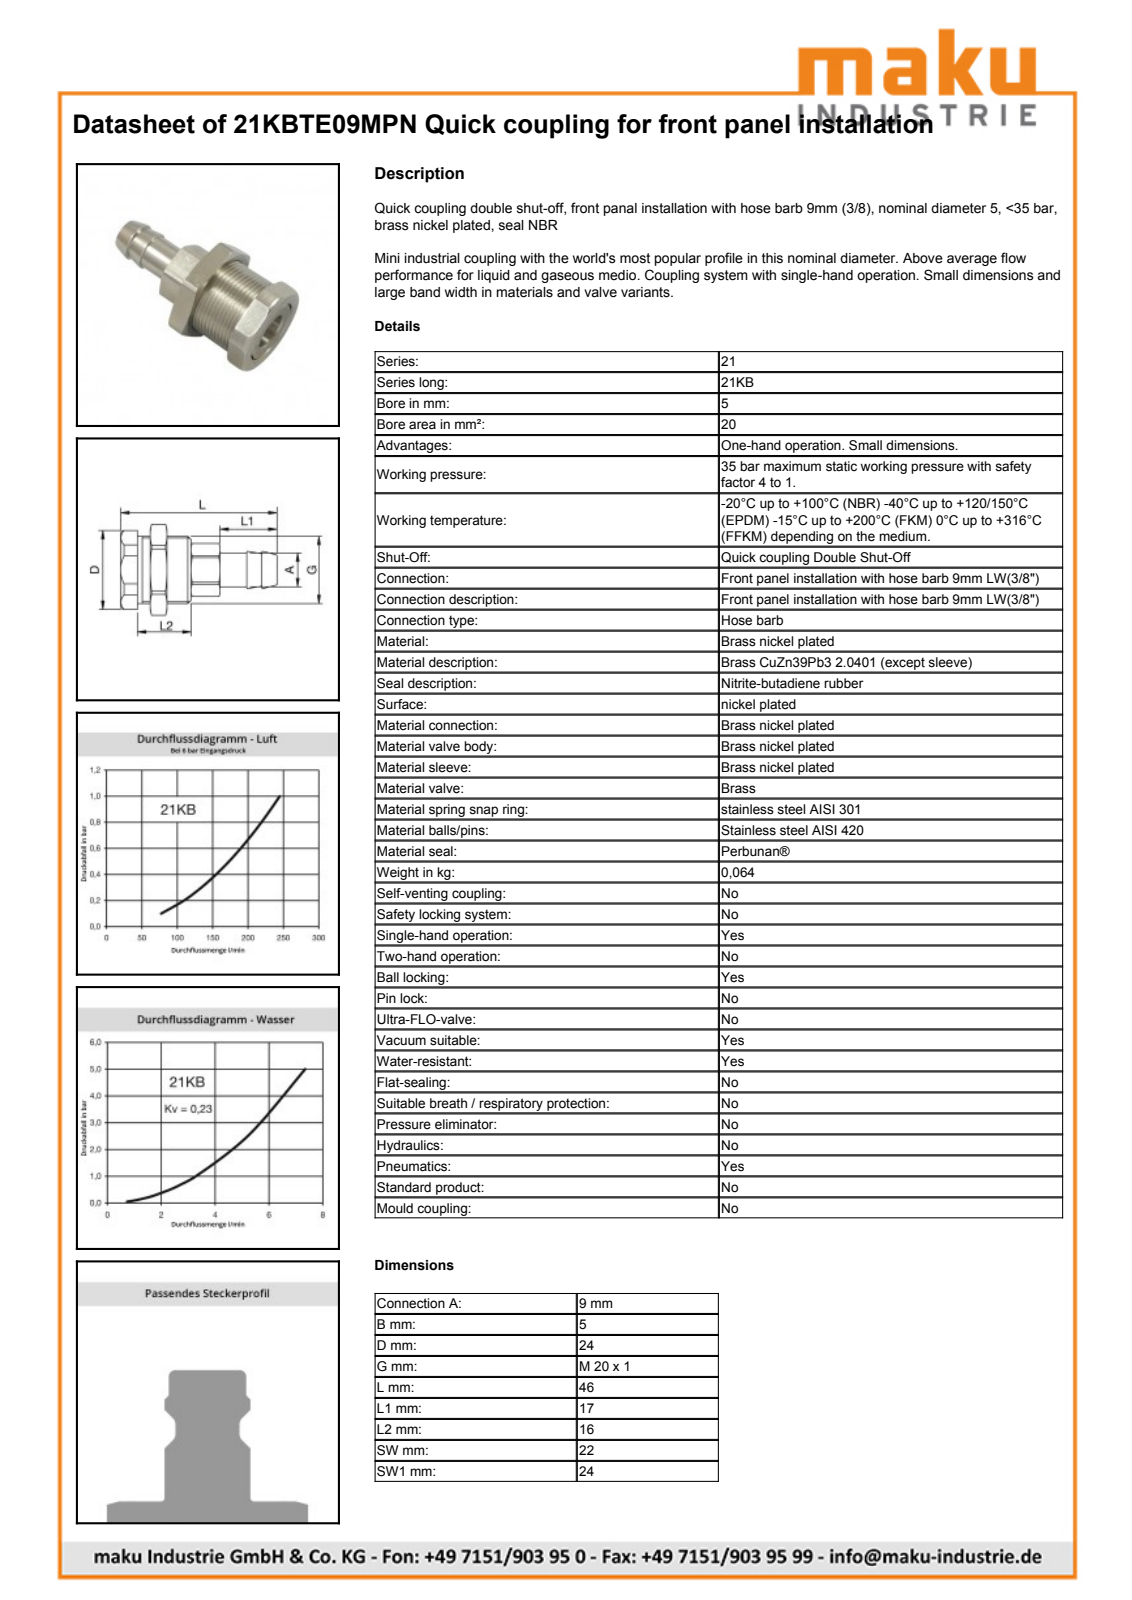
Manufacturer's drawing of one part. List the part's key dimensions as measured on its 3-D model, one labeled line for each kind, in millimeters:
Part name (STEP PRODUCT): D111914
STEP written by: Autodesk Inventor 2013 (AUTOMOTIVE_DESIGN)
Units: millimetres
Bodies: 1 solid, 137 faces (44 planar, 45 cylindrical, 48 other)
Overall size (bounding box): 46.2 × 27.05 × 24
Volume: 9 334 mm³ · Surface area: 5 814 mm²
Round holes (diameter × count): ⌀10.4 ×1, ⌀10.45 ×1, ⌀10.7 ×1, ⌀12 ×1, ⌀14.4 ×1, ⌀14.75 ×1, ⌀16 ×1, ⌀16.2 ×1
Round bosses / shafts (diameter × count): ⌀20 ×1, ⌀14 ×1, ⌀11.4 ×1, ⌀10.52 ×1, ⌀9.05 ×1
Partial cylindrical surfaces — rounded edges, fillets, slot ends (radius × count): R7.9 ×1, R11.75 ×1, R13.53 ×1
Main face-to-face distances: 5, 19, 10, 1, 23, 4, 18, 14, 24, 15
